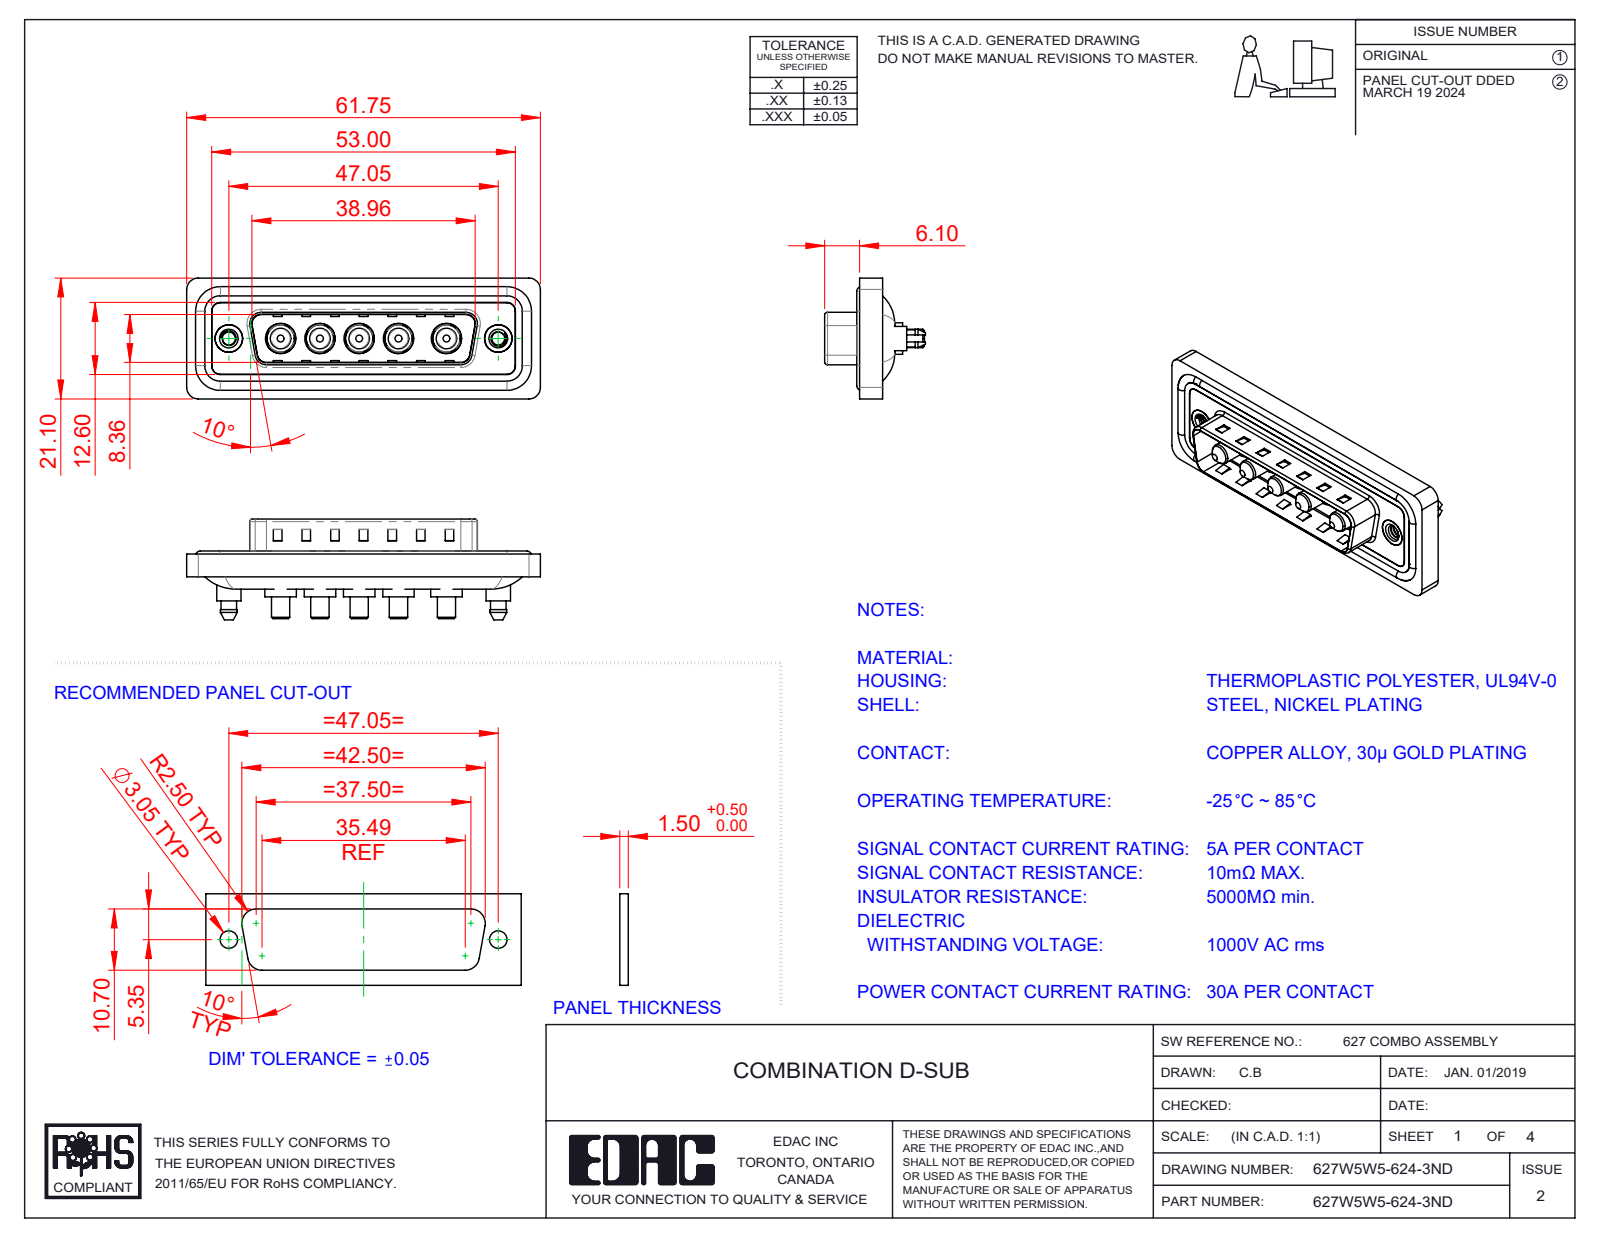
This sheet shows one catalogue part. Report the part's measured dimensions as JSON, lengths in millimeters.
{"part_name": "627Combo Housing_5W5; Power Pin_30A S; 627W5W5-624-3ND; 627Combo Waterproof Housing_25 Contacts (+4 more)", "step_written_by": "SolidWorks 2023 (CONFIG_CONTROL_DESIGN)", "units": "millimeters", "bodies": {"solids": 17, "faces": 736, "planar": 275, "cylindrical": 323, "other": 138}, "overall_size": [61.75, 21.1, 17.6], "volume_mm3": 7643, "surface_area_mm2": 12155, "round_holes": [[4.85, 5], [5.3, 5], [2.26, 2], [4, 2], [4.8, 2], [5, 2]], "round_bosses_or_shafts": [[5.5, 5], [5.2, 5], [4.75, 5], [3.75, 5], [3.6, 5], [3.2, 5], [1.6, 4], [5.4, 2]], "partial_cylinders_radius": [[1.5, 24], [2, 18], [1.6, 10], [0.5, 8], [2.1, 5], [0.25, 4], [0.6, 4], [0.65, 4]], "face_to_face_distances": [0.4, 1.5, 3.1, 1.1, 0.5, 1.6, 2.9, 0.82, 9.58, 5.65], "hole_center_spacings": [6.86, 9.04, 13.73, 38.01, 6.87, 8.37, 8.38, 9.05]}
